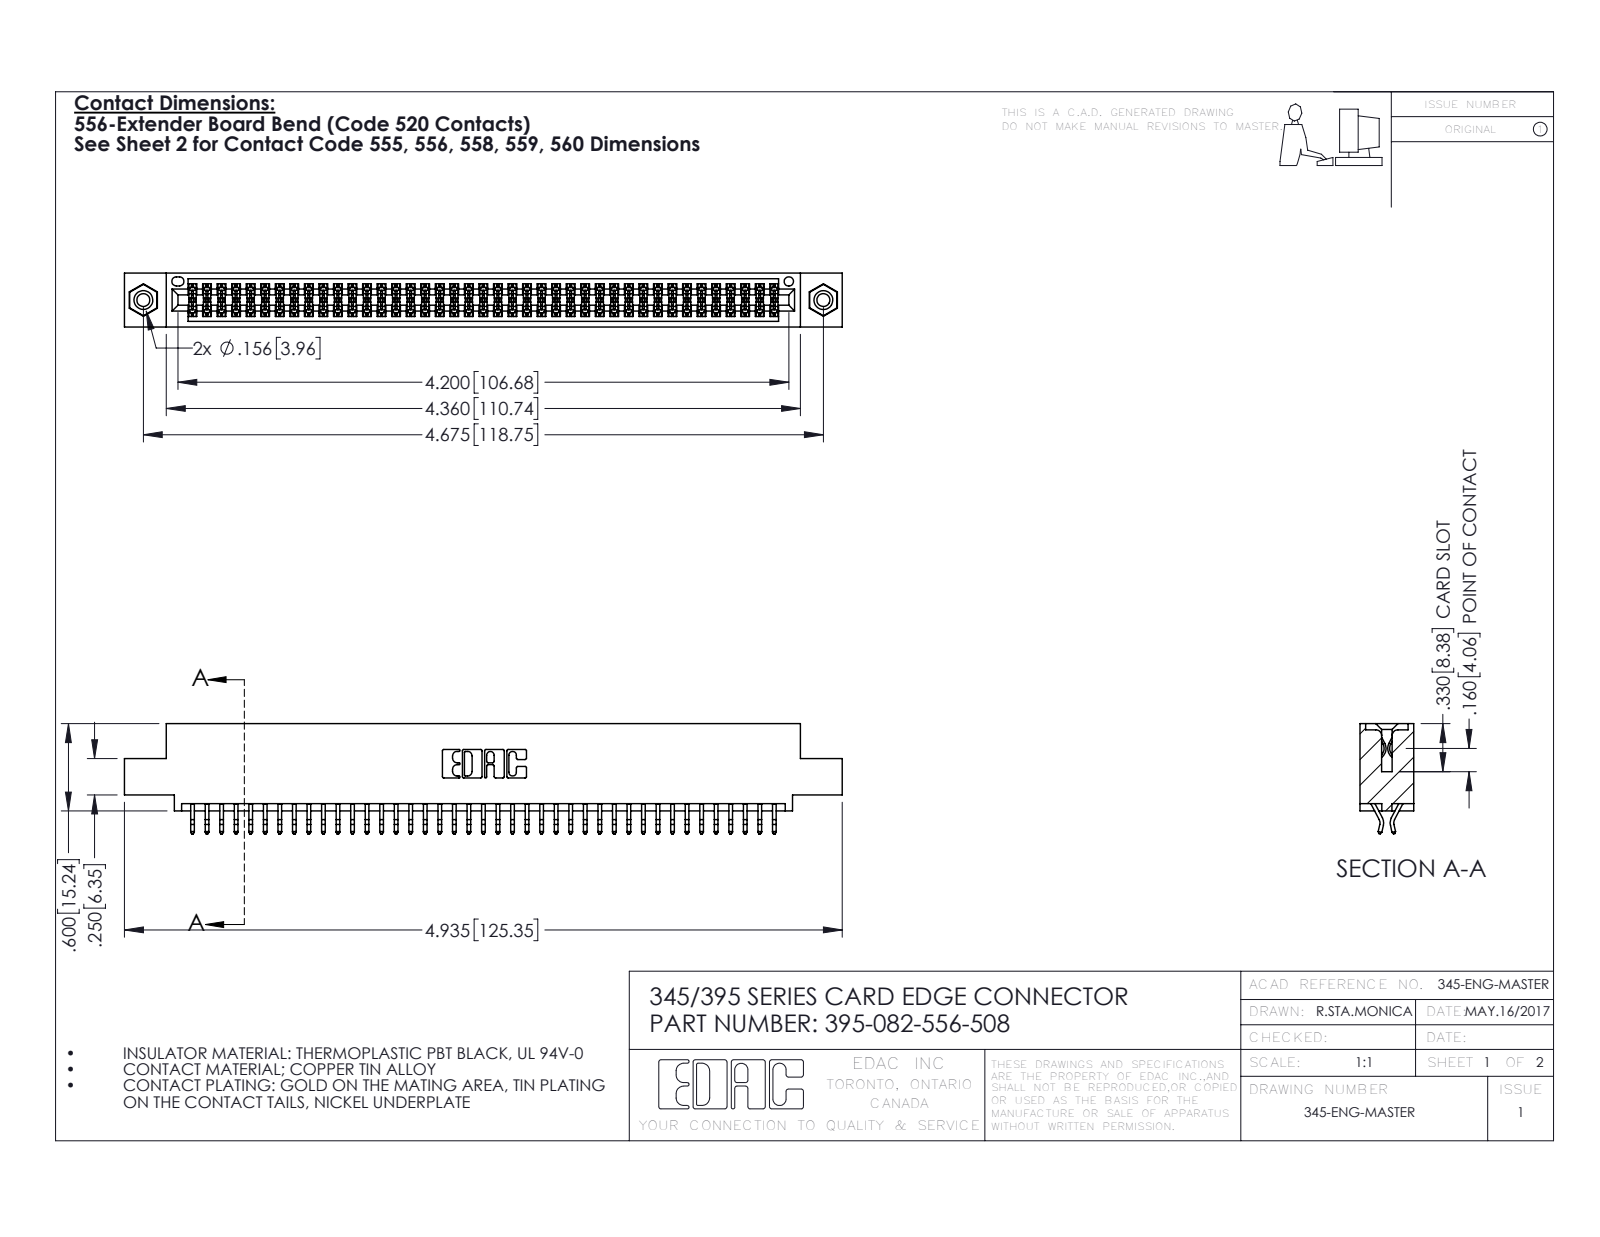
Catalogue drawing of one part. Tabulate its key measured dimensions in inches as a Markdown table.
| quantity | value |
| --- | --- |
| part name | 345-250-001_345-250-003-102; 395-082-556-508; 345 Part_0.110 Offset - 0.156 Dia-TI; 345-292-001_556 Tail |
| STEP written by | SolidWorks 2016 (CONFIG_CONTROL_DESIGN) |
| units | inches |
| bodies | 85 solids, 4782 faces (3150 planar, 1616 cylindrical, 16 other) |
| overall size | 4.935 × 0.757 × 0.37 |
| volume | 0.737 in³ |
| surface area | 27.71 in² |
| round holes (diameter × count) | 0.089 × 2, 0.125 × 2, 0.156 × 2, 0.064 × 1 |
| round bosses / shafts (diameter × count) | 0.155 × 2 |
| partial cylindrical surfaces (radius × count) | 0.006 × 123, 0.01 × 22, 0.007 × 6, 0.031 × 6, 0.026 × 3, 0.01 × 2, 0.014 × 2, 0.019 × 2 |
| main face-to-face distances | 0.072, 0.298, 0.37, 0.2, 0.025, 0.098, 0.272, 0.225, 0.175, 0.149 |
| hole center spacings | 0.27, 4.439, 4.675 |
